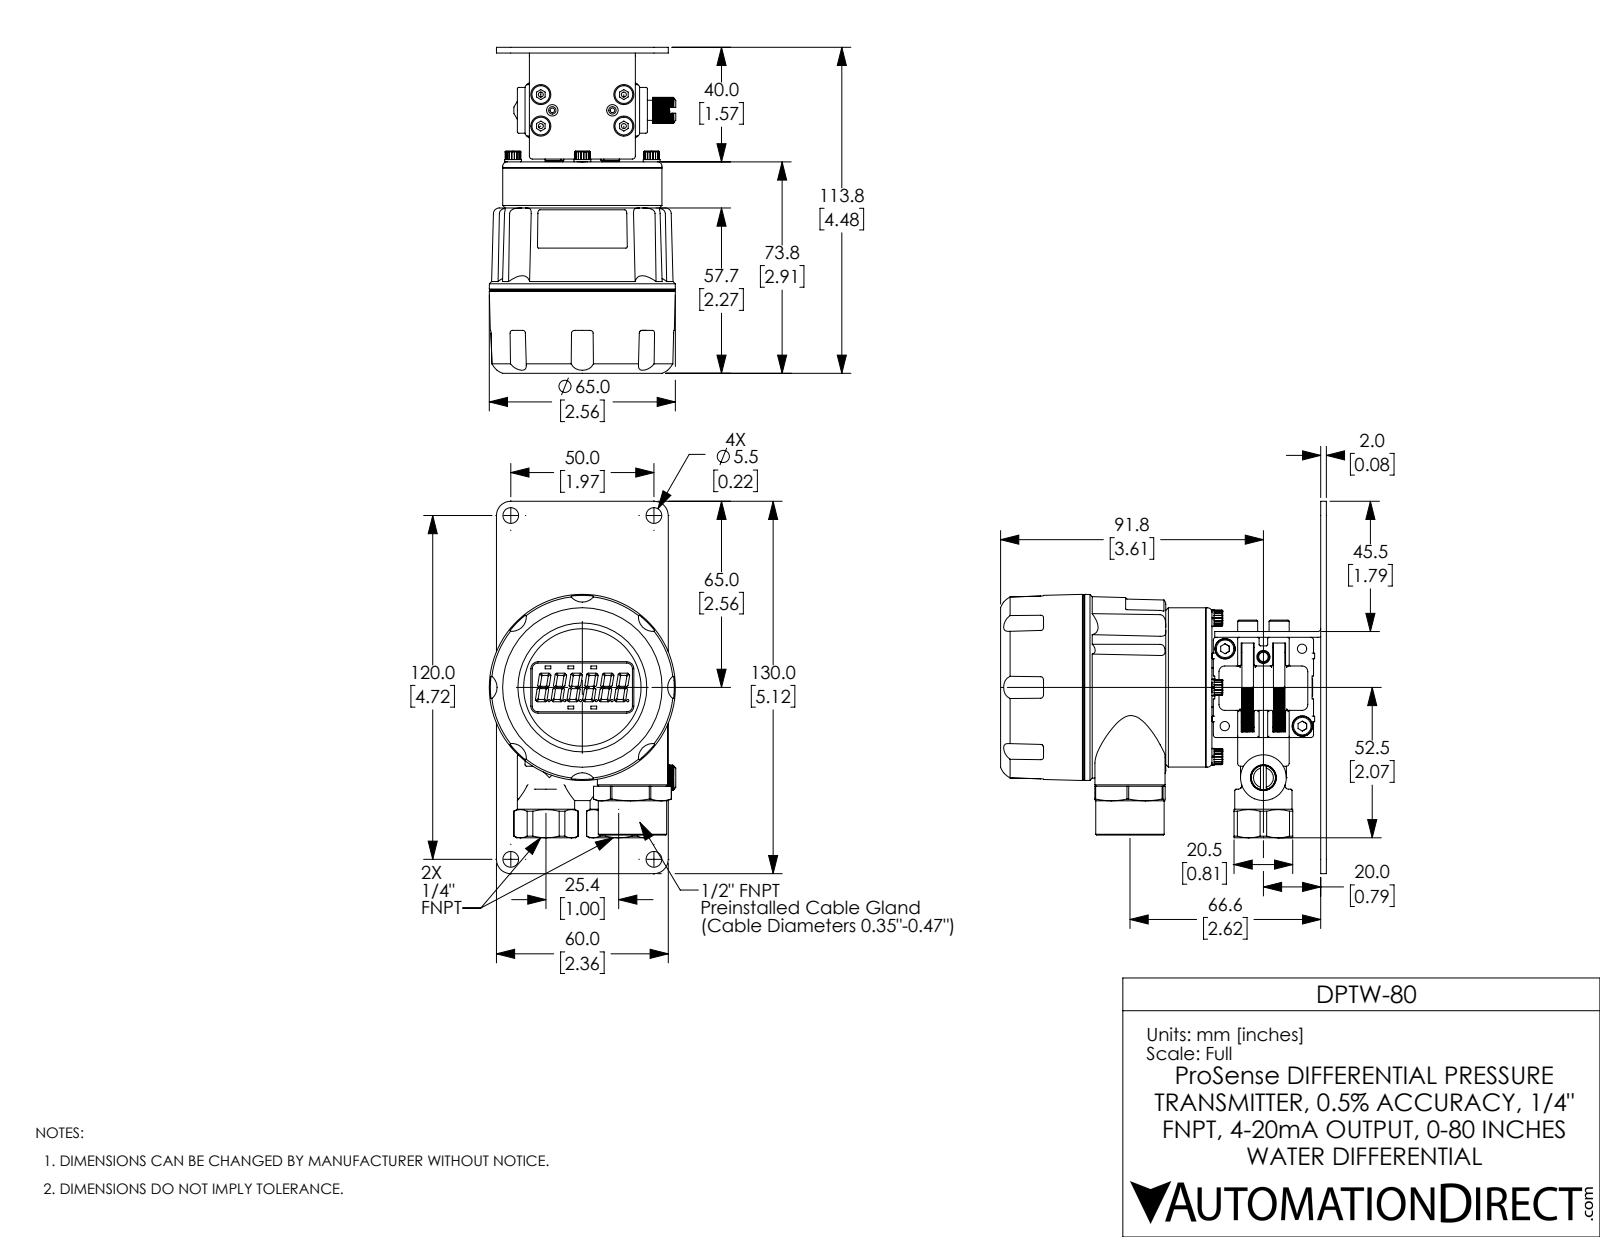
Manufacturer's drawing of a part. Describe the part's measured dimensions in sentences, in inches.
The part is named "DPTW-400". Its 3-D file was written by "SolidWorks 2017 (AUTOMOTIVE_DESIGN)". It is 1 solid with 2436 faces: 1055 planar, 992 cylindrical and 389 other. Overall it measures 5.118 by 4.48 by 2.563 inches. Its volume is 17.03 cubic inches and its surface area 97.34 square inches. Round holes: 6 of diameter 0.031, 4 of diameter 0.118, 4 of diameter 0.126, 4 of diameter 0.128, 4 of diameter 0.169, 4 of diameter 0.177, 4 of diameter 0.217, 3 of diameter 0.157, 2 of diameter 0.047, 2 of diameter 0.063, 2 of diameter 0.256, 2 of diameter 0.433. Round bosses or shafts: 5 of diameter 0.276, 4 of diameter 0.282, 4 of diameter 0.26, 4 of diameter 0.236, 4 of diameter 0.232, 4 of diameter 0.217, 4 of diameter 0.157, 2 of diameter 0.787. Partial cylindrical surfaces (rounded edges, fillets, slot ends): 64 of radius 0.02, 42 of radius 0.008, 21 of radius 0.039, 12 of radius 0.024, 12 of radius 0.031, 8 of radius 0.016, 8 of radius 0.079, 4 of radius 0.157. The main face-to-face distances are 0.079, 1.496, 1.575, 1.378, 0.807, 0.157, 4.48, 4.402, 2.906, 0.217. The hole center spacings are 0.217, 0.433, 0.228, 0.246, 0.268, 0.866, 1.008, 1.046.
